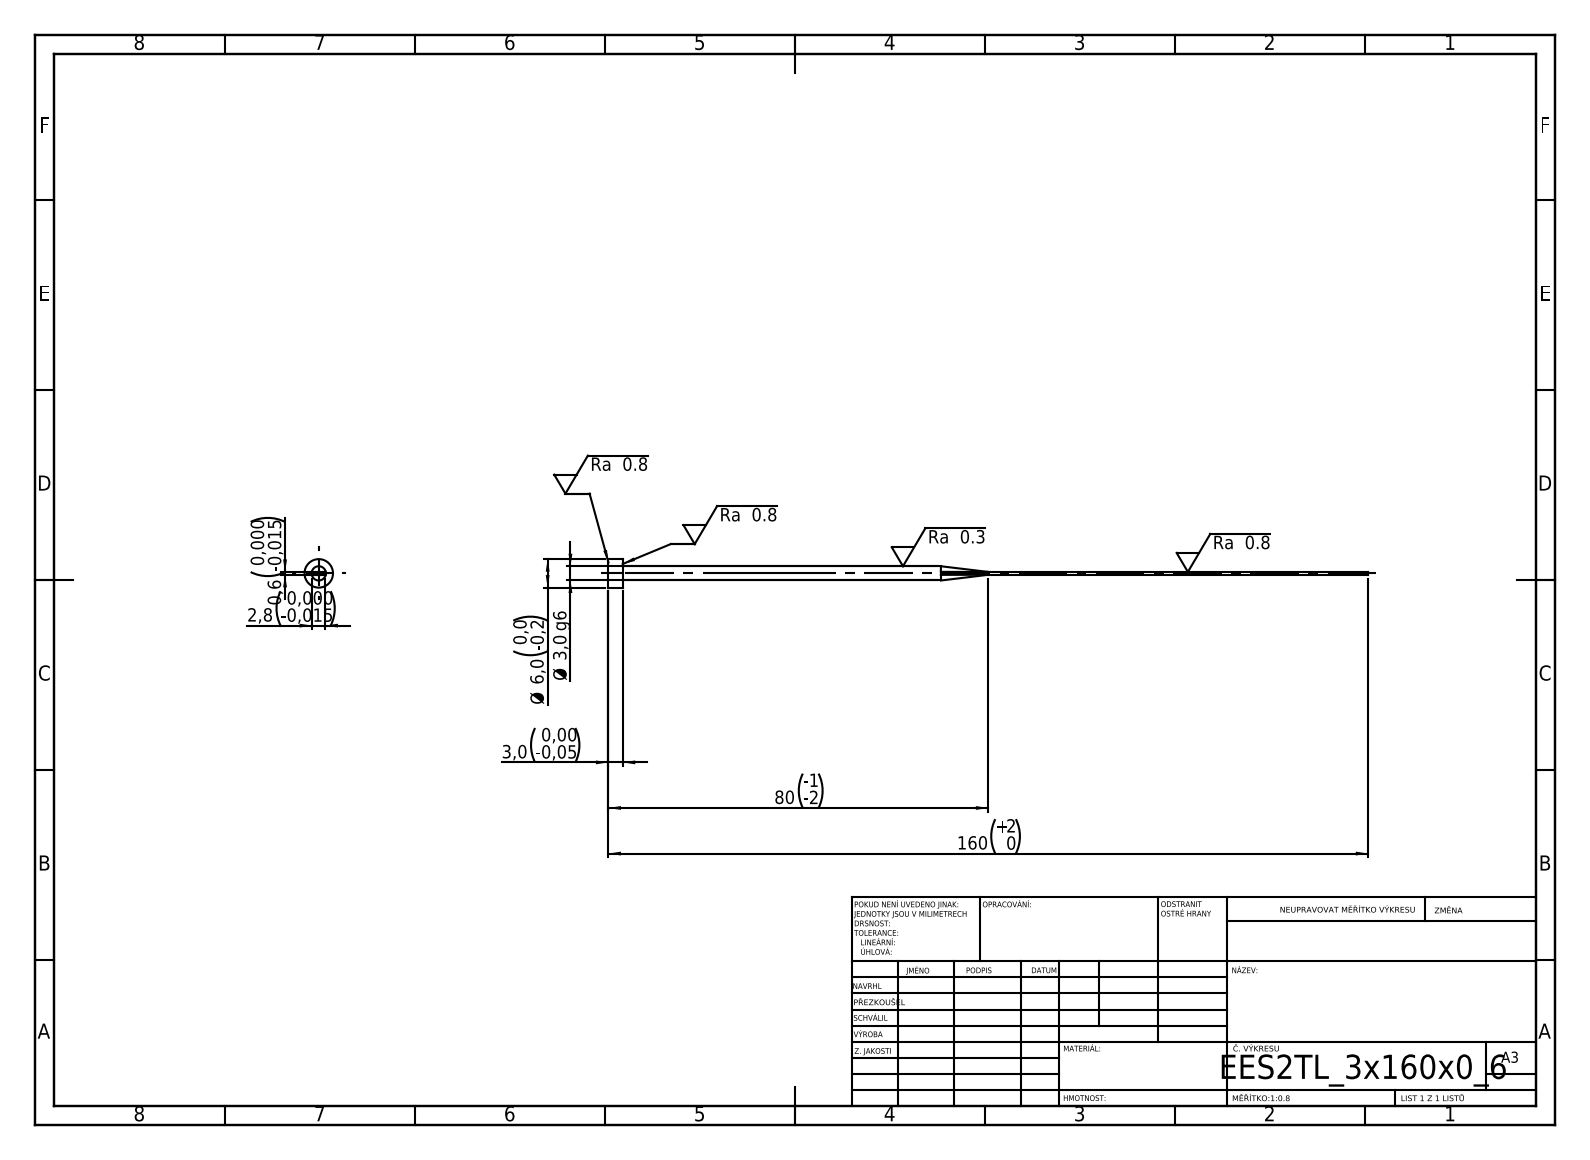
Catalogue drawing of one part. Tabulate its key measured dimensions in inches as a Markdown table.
| quantity | value |
| --- | --- |
| STEP written by | SolidWorks 2019 (CONFIG_CONTROL_DESIGN) |
| units | inches |
| bodies | 1 solid, 15 faces (7 planar, 4 cylindrical, 4 other) |
| overall size | 6.299 × 0.236 × 0.236 |
| volume | 0.045 in³ |
| surface area | 2.11 in² |
| round bosses / shafts (diameter × count) | 0.236 × 1, 0.118 × 1 |
| main face-to-face distances | 0.024, 0.11, 0.118, 6.299, 6.181 |
